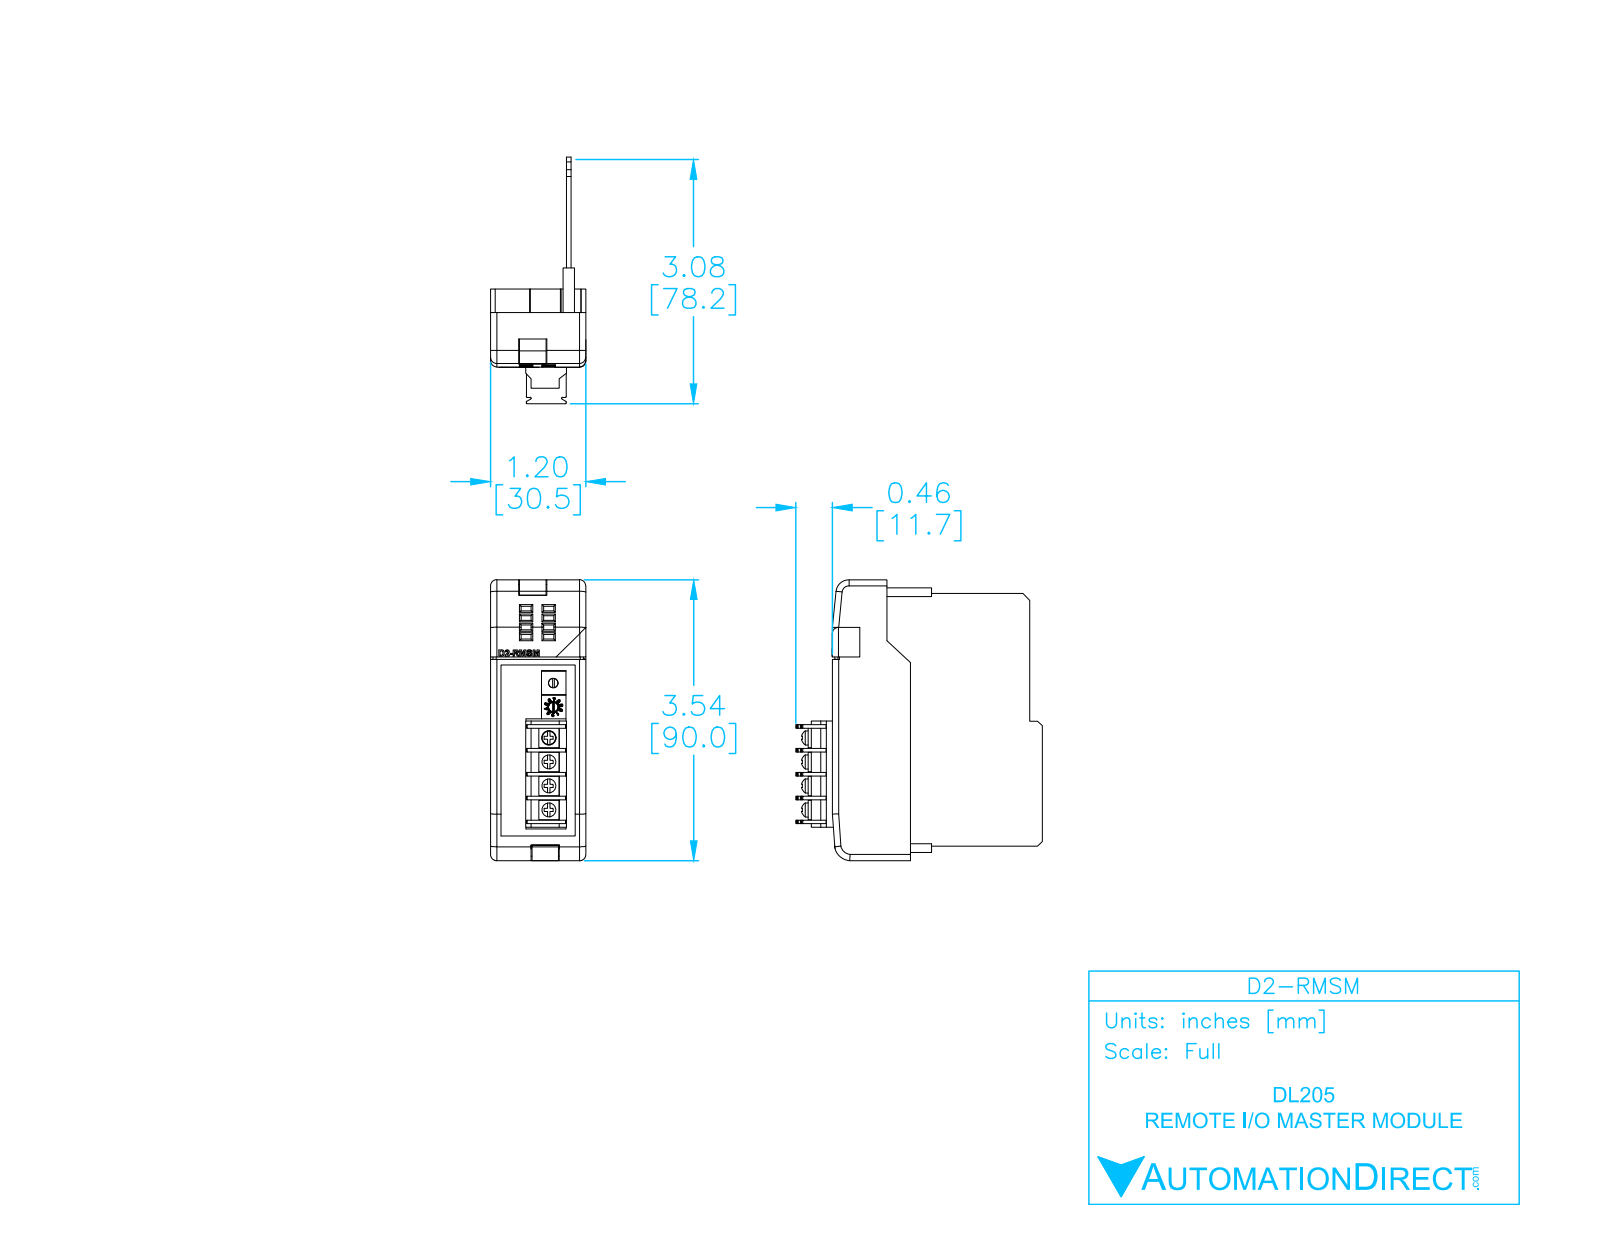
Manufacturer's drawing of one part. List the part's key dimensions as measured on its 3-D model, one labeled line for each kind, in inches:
Part name (STEP PRODUCT): D2-RMSM
STEP written by: SolidWorks 2009 (AUTOMOTIVE_DESIGN)
Units: inches
Bodies: 7 solids, 658 faces (442 planar, 150 cylindrical, 66 other)
Overall size (bounding box): 3.543 × 3.11 × 1.203
Volume: 1.299 in³ · Surface area: 45.4 in²
Round holes (diameter × count): ⌀0.118 ×2
Round bosses / shafts (diameter × count): ⌀0.177 ×4
Partial cylindrical surfaces — rounded edges, fillets, slot ends (radius × count): R0.02 ×28, R0.01 ×14, R0.079 ×11, R0.039 ×2, R0.103 ×1, R0.149 ×1, R0.162 ×1, R0.208 ×1
Main face-to-face distances: 0.059, 0.186, 0.127, 0.245, 0.956, 1.142, 0.02, 1.015, 1.201, 0.897
Hole centre spacings: 0.305
